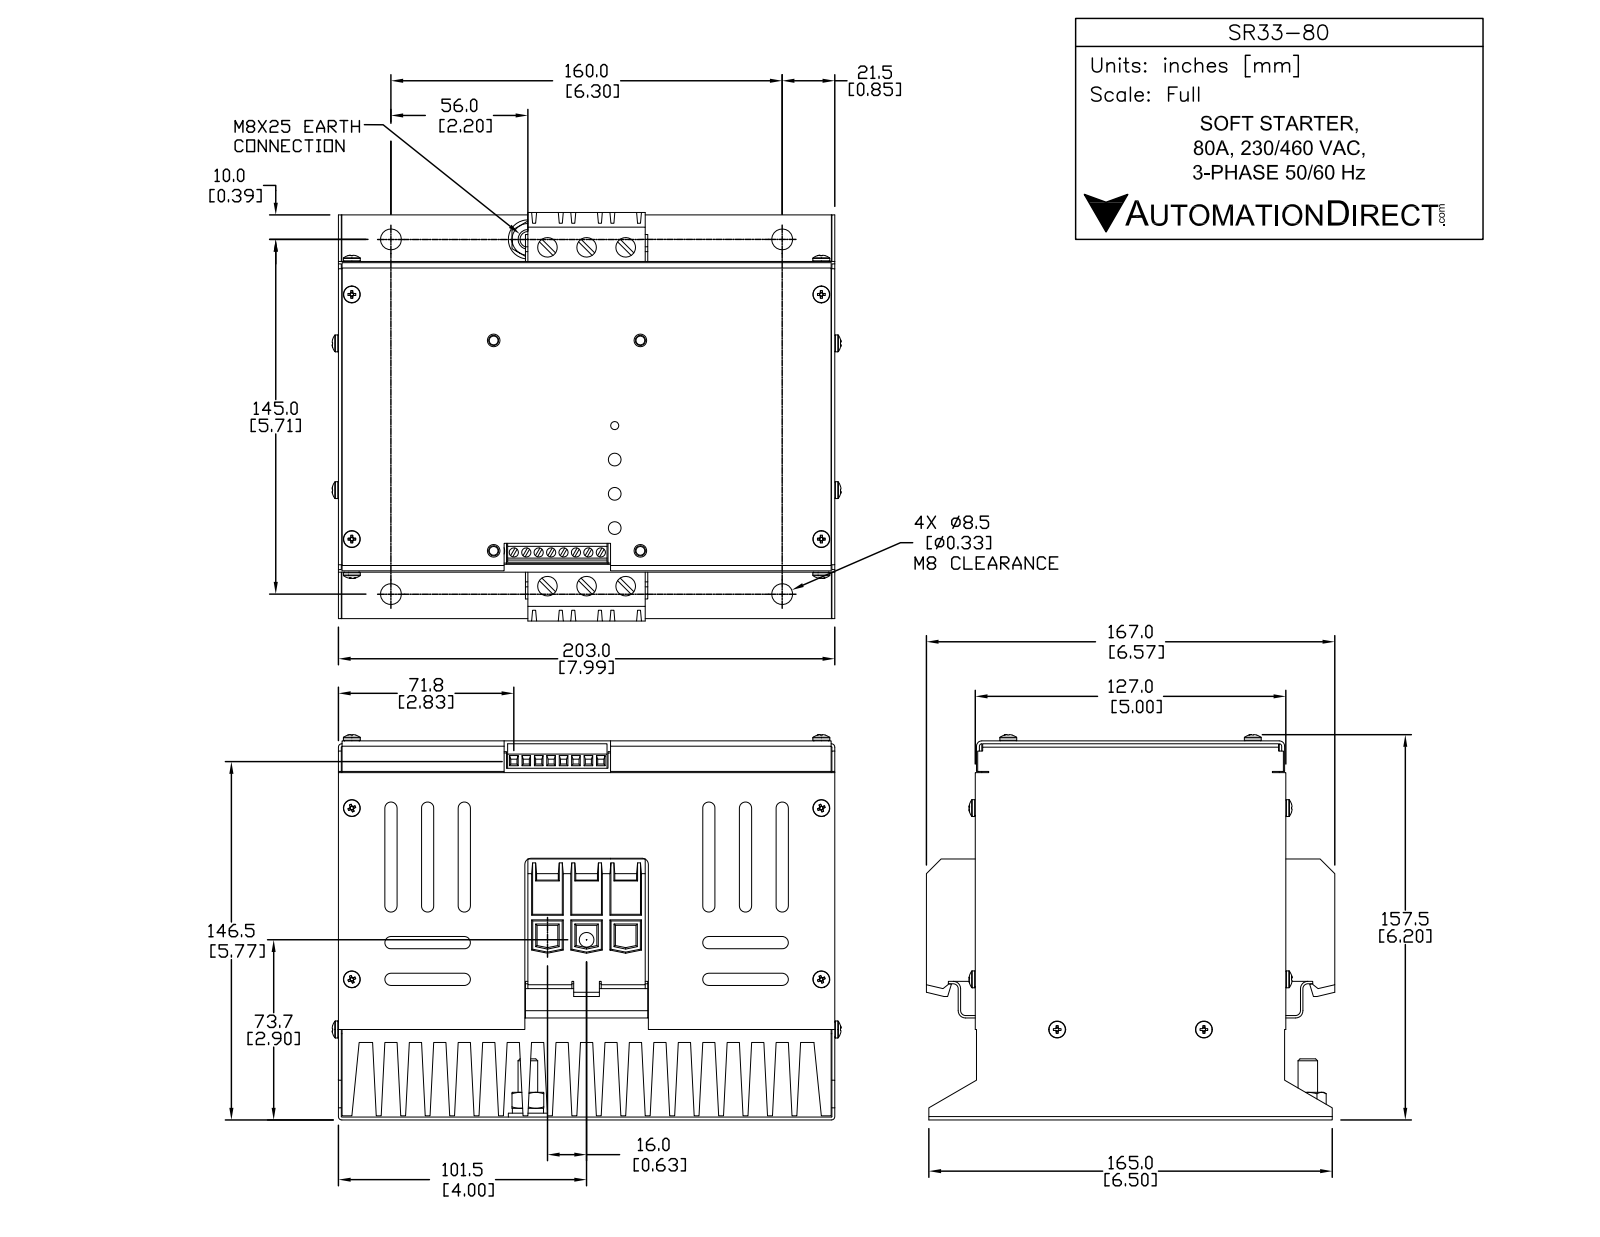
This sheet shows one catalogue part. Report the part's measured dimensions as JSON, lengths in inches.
{"part_name": "SR33-80", "step_written_by": "SolidWorks 2013 (AUTOMOTIVE_DESIGN)", "units": "inches", "bodies": {"solids": 1, "faces": 838, "planar": 611, "cylindrical": 153, "other": 74}, "overall_size": [7.992, 6.496, 6.22], "volume_in3": 201.3, "surface_area_in2": 758.8, "round_holes": [[0.15, 8], [0.197, 6], [0.335, 4]], "round_bosses_or_shafts": [[0.272, 8], [0.472, 1], [0.236, 1]], "partial_cylinders_radius": [[0.02, 24], [0.098, 20], [0.079, 8], [0.039, 6]], "face_to_face_distances": [0.393, 0.787, 1.18, 1.573, 1.967, 2.36, 2.753, 3.146, 3.54, 3.933], "hole_center_spacings": [0.194, 0.387, 0.581, 0.591, 0.775, 2.564, 3.154, 3.743]}
